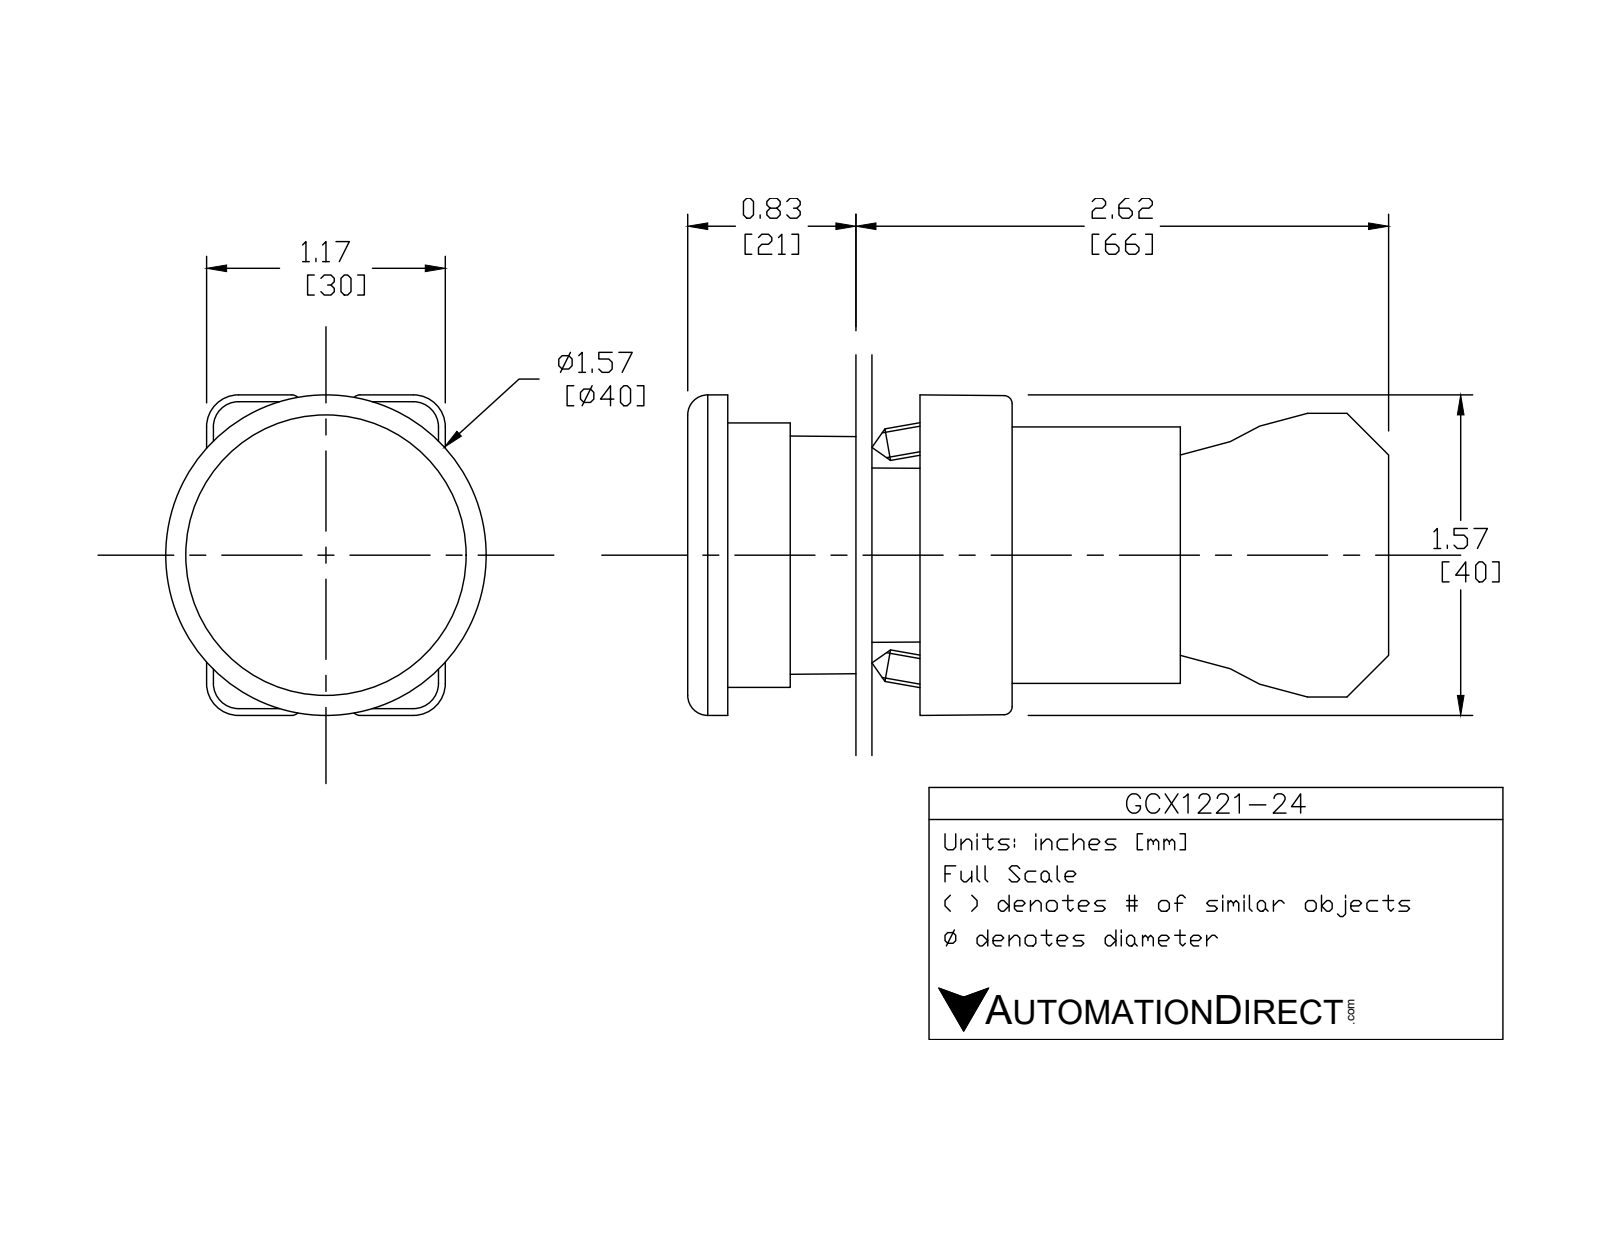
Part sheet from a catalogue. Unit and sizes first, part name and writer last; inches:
Units: inches
Overall size (bounding box): 3.469 × 1.581 × 1.575
Round holes (diameter × count): ⌀0.079 ×2, ⌀0.124 ×2, ⌀0.13 ×2, ⌀0.087 ×1, ⌀0.197 ×1, ⌀0.469 ×1, ⌀0.878 ×1, ⌀0.888 ×1, ⌀1.024 ×1, ⌀1.181 ×1
Round bosses / shafts (diameter × count): ⌀0.157 ×4, ⌀1.299 ×1, ⌀1.175 ×1, ⌀0.945 ×1, ⌀0.856 ×1, ⌀0.78 ×1, ⌀0.504 ×1
Partial cylindrical surfaces — rounded edges, fillets, slot ends (radius × count): R0.059 ×24, R0.041 ×12, R0.124 ×12, R0.157 ×12, R0.039 ×8, R0.128 ×2, R0.02 ×1, R0.063 ×1
Main face-to-face distances: 0.827, 2.445, 1.618, 0.579, 2.287, 1.461, 0.157, 0.587, 0.031, 1.165
Hole centre spacings: 0.236, 0.539, 0.472, 0.484
Volume: 2.895 in³ · Surface area: 40.89 in²
Bodies: 7 solids, 431 faces (252 planar, 146 cylindrical, 33 other)
Part name (STEP PRODUCT): GCX1221-24; GCX122X OPERATOR; ECX1050; ECX1029-2 (+1 more)
STEP written by: SolidWorks 2016 (AUTOMOTIVE_DESIGN)
